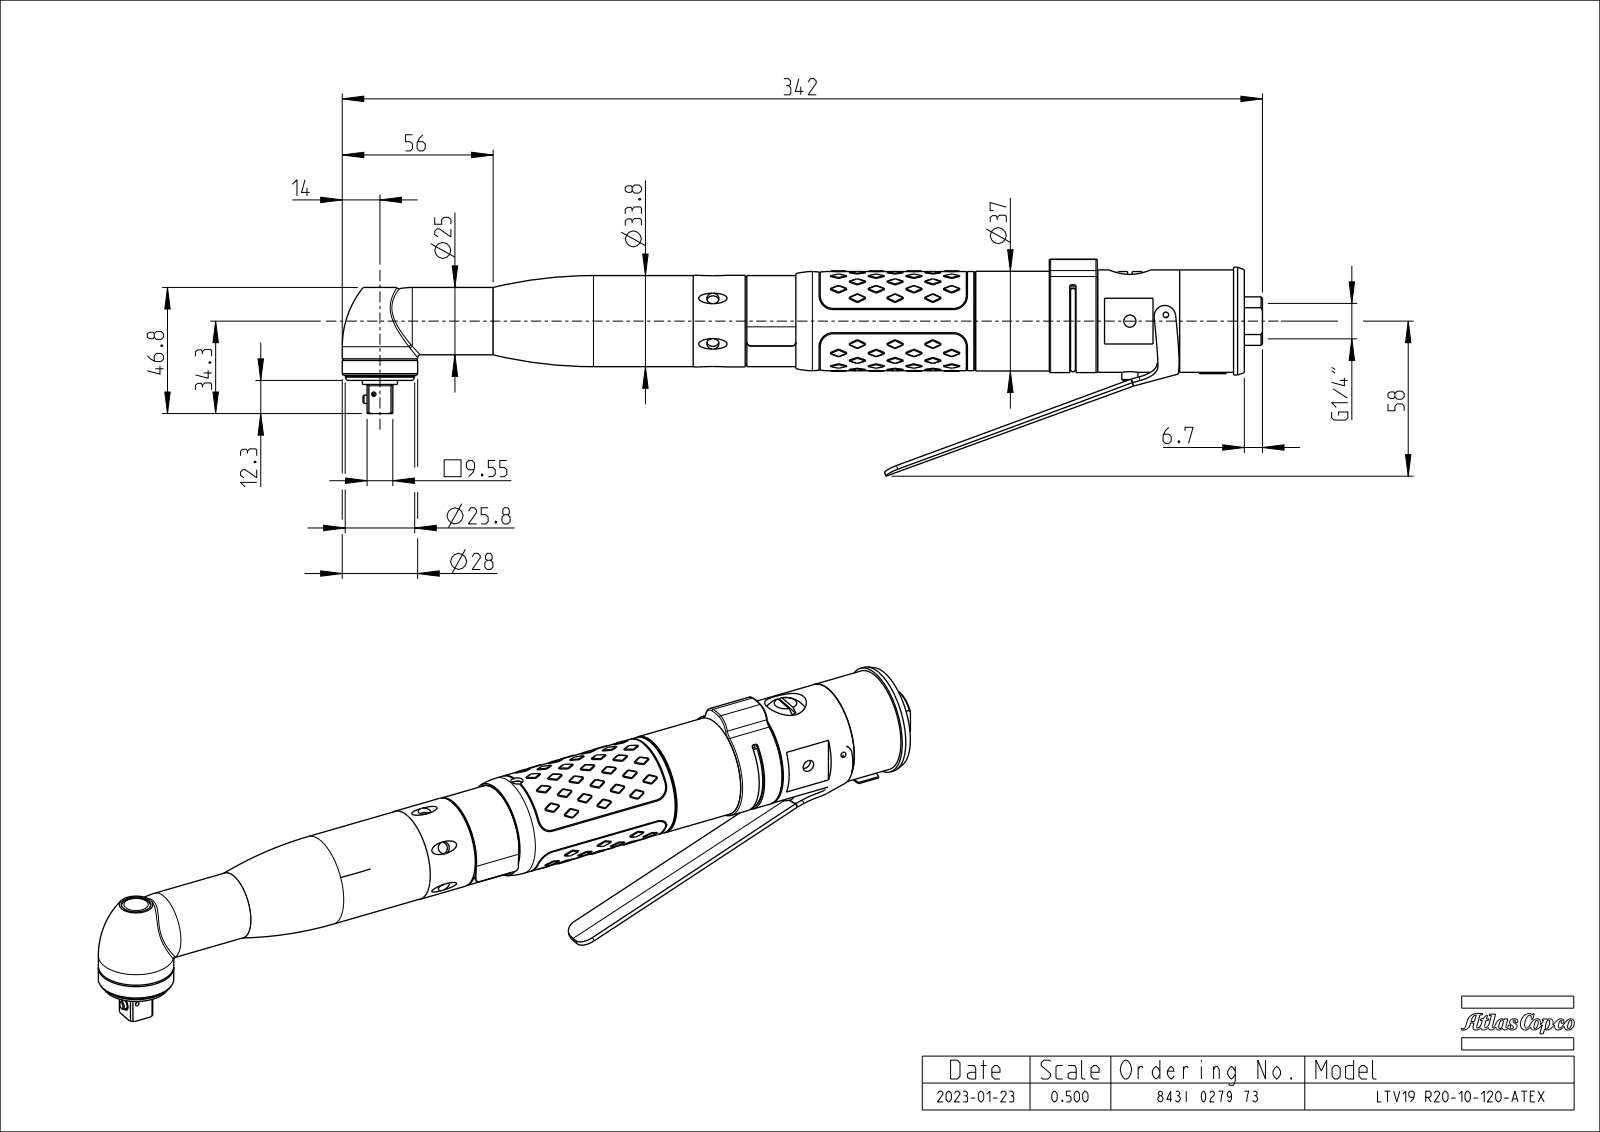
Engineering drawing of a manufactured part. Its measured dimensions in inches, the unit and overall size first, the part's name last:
Units: inches
Overall size (bounding box): 13.45 × 3.171 × 1.575
Round holes (diameter × count): ⌀0.118 ×12, ⌀0.177 ×5, ⌀0.11 ×4, ⌀0.059 ×1, ⌀0.122 ×1, ⌀0.451 ×1, ⌀0.52 ×1, ⌀0.604 ×1, ⌀0.61 ×1, ⌀0.728 ×1, ⌀1.055 ×1, ⌀1.264 ×1
Round bosses / shafts (diameter × count): ⌀1.575 ×1, ⌀1.504 ×1, ⌀1.496 ×1, ⌀1.457 ×1, ⌀1.449 ×1, ⌀1.433 ×1, ⌀1.339 ×1, ⌀1.331 ×1
Partial cylindrical surfaces — rounded edges, fillets, slot ends (radius × count): R0.02 ×11, R0.031 ×6, R0.008 ×4, R0.028 ×2, R0.039 ×2, R0.045 ×2, R0.059 ×2, R0.157 ×2
Main face-to-face distances: 2.142, 0.02, 1.339, 0.079, 2.15, 3.933, 1.791, 1.783, 3.937, 1.795
Hole centre spacings: 0.63, 0.891, 1.217, 0.326, 1.091, 0.326, 0.384, 0.543
Volume: 19.19 in³ · Surface area: 79.83 in²
Bodies: 2 solids, 1255 faces (98 planar, 253 cylindrical, 904 other)
Part name (STEP PRODUCT): EXT_COMP_SW0007
STEP written by: CREO PARAMETRIC BY PTC INC, 2020281 (CONFIG_CONTROL_DESIGN)
